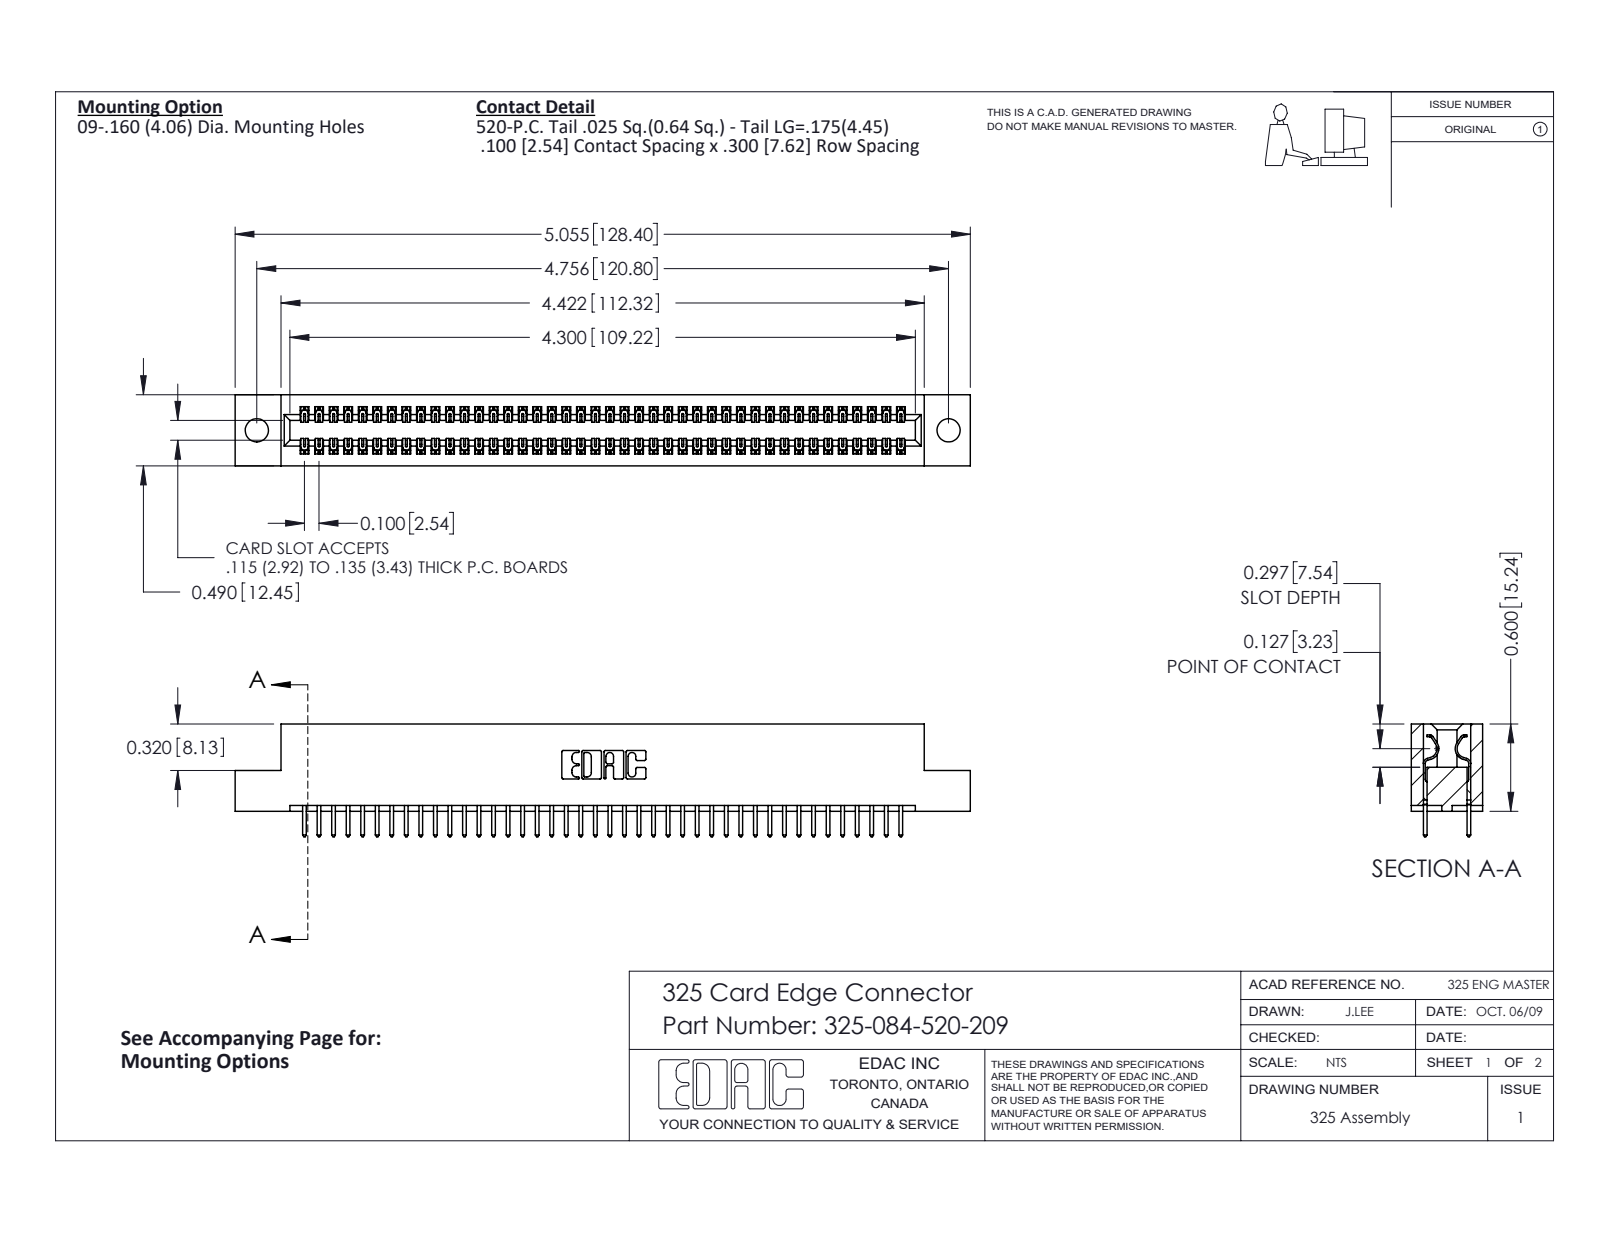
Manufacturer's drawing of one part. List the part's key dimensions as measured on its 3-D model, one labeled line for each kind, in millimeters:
Part name (STEP PRODUCT): 325-084-520-209; 325-292-001_325-293-120; 325 Part_.160 TH
STEP written by: SolidWorks 2016 (CONFIG_CONTROL_DESIGN)
Units: millimetres
Bodies: 85 solids, 4482 faces (3094 planar, 1388 cylindrical, 0 other)
Overall size (bounding box): 128.4 × 19.7 × 12.4
Volume: 16 300 mm³ · Surface area: 19 520 mm²
Round holes (diameter × count): ⌀4.1 ×2
Partial cylindrical surfaces — rounded edges, fillets, slot ends (radius × count): R0.2 ×126, R0.3 ×84, R0.3 ×22, R0.2 ×6, R0.8 ×6, R0.7 ×3, R0.4 ×2, R0.6 ×2
Main face-to-face distances: 2.1, 10.3, 7.6, 12.4, 2.7, 9.7, 0.6, 8.3, 7, 14.2
Hole centre spacings: 120.8
